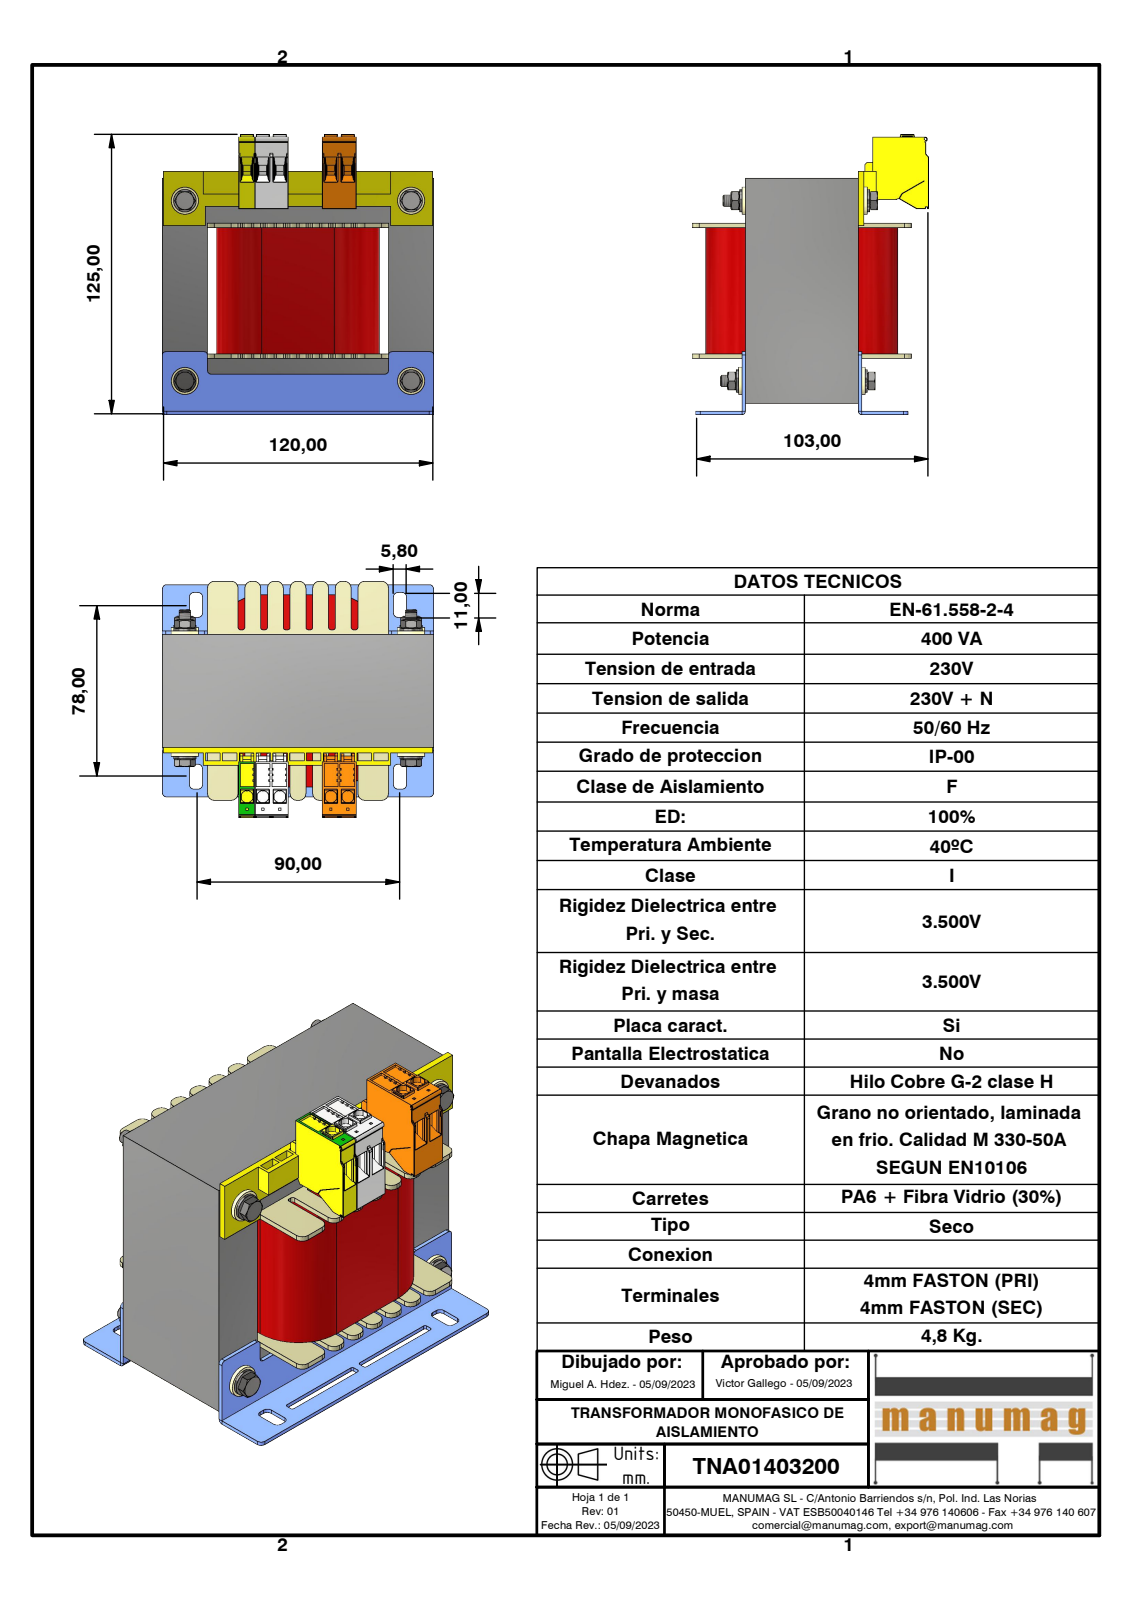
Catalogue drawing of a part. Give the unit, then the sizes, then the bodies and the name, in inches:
Units: inches
Overall size (bounding box): 4.902 × 4.724 × 4.12
Round holes (diameter × count): ⌀0.163 ×4, ⌀0.197 ×4, ⌀0.209 ×4, ⌀0.26 ×4, ⌀0.268 ×2
Round bosses / shafts (diameter × count): ⌀0.472 ×4, ⌀0.394 ×4, ⌀0.264 ×4, ⌀0.232 ×4, ⌀0.18 ×4
Partial cylindrical surfaces — rounded edges, fillets, slot ends (radius × count): R0.006 ×214, R0.008 ×58, R0.039 ×28, R0.118 ×28, R0.079 ×20, R0.031 ×17, R0.02 ×14, R0.012 ×6
Main face-to-face distances: 3.15, 0.787, 1.575, 1.969, 2.362, 3.937, 0.059, 0.63, 2.205, 3.346
Hole centre spacings: 3.15, 3.937, 5.042
Volume: 46.02 in³ · Surface area: 247.5 in²
Bodies: 32 solids, 5330 faces (4334 planar, 692 cylindrical, 304 other)
Part name (STEP PRODUCT): TNA01403200; EI120 x 100 - 50 (Rc40); EI120; centrador M5 (+8 more)
STEP written by: Autodesk Inventor 2023 (AUTOMOTIVE_DESIGN)
